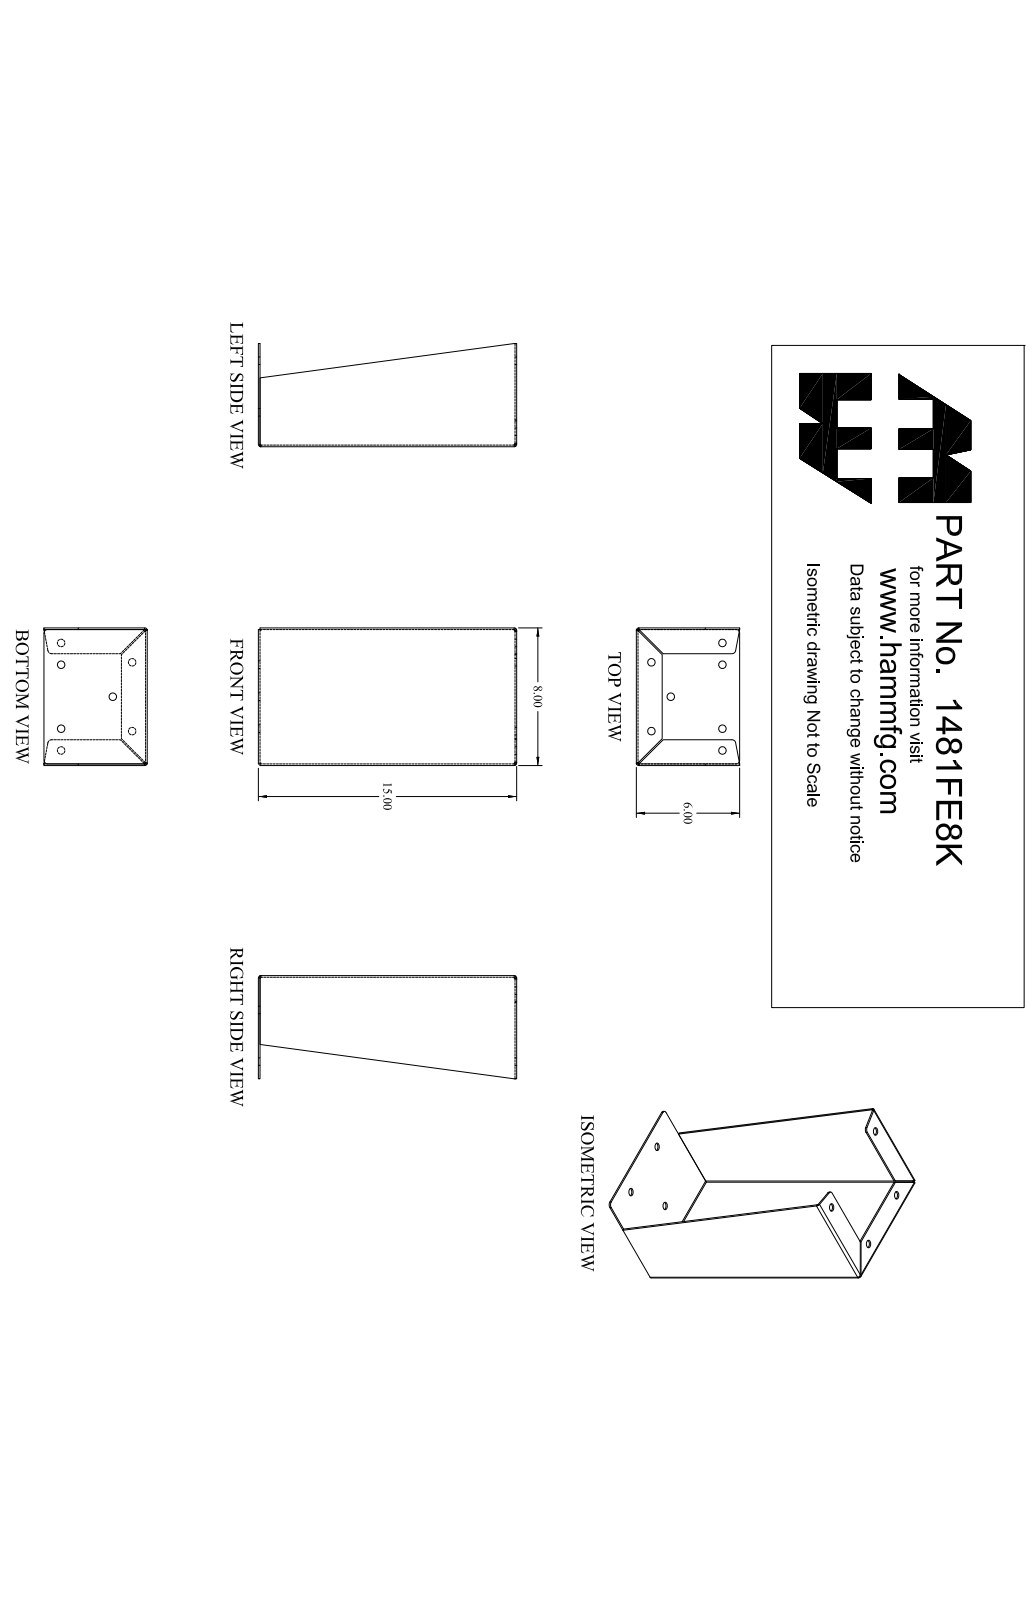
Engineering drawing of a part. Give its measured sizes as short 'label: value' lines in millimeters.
name: 1481FE8K_Default
written by: SolidWorks 2019 (CONFIG_CONTROL_DESIGN)
unit: mm
bodies: 1 solid, 78 faces (42 planar, 30 cylindrical, 6 other)
size: 381 × 203.2 × 152.4
volume: 517 000 mm³; area: 434 100 mm²
holes: 7× ⌀11.1
rounds: 6× R1.2, 6× R3.6, 4× R5.6
face distances: 2.4, 200.8, 203.2, 198.4, 2.4, 376.2, 378.6, 378.6, 381, 35.7
hole spacings: 32.2, 58.3, 89.6, 104.8, 108.6, 110, 126.6, 143.5
